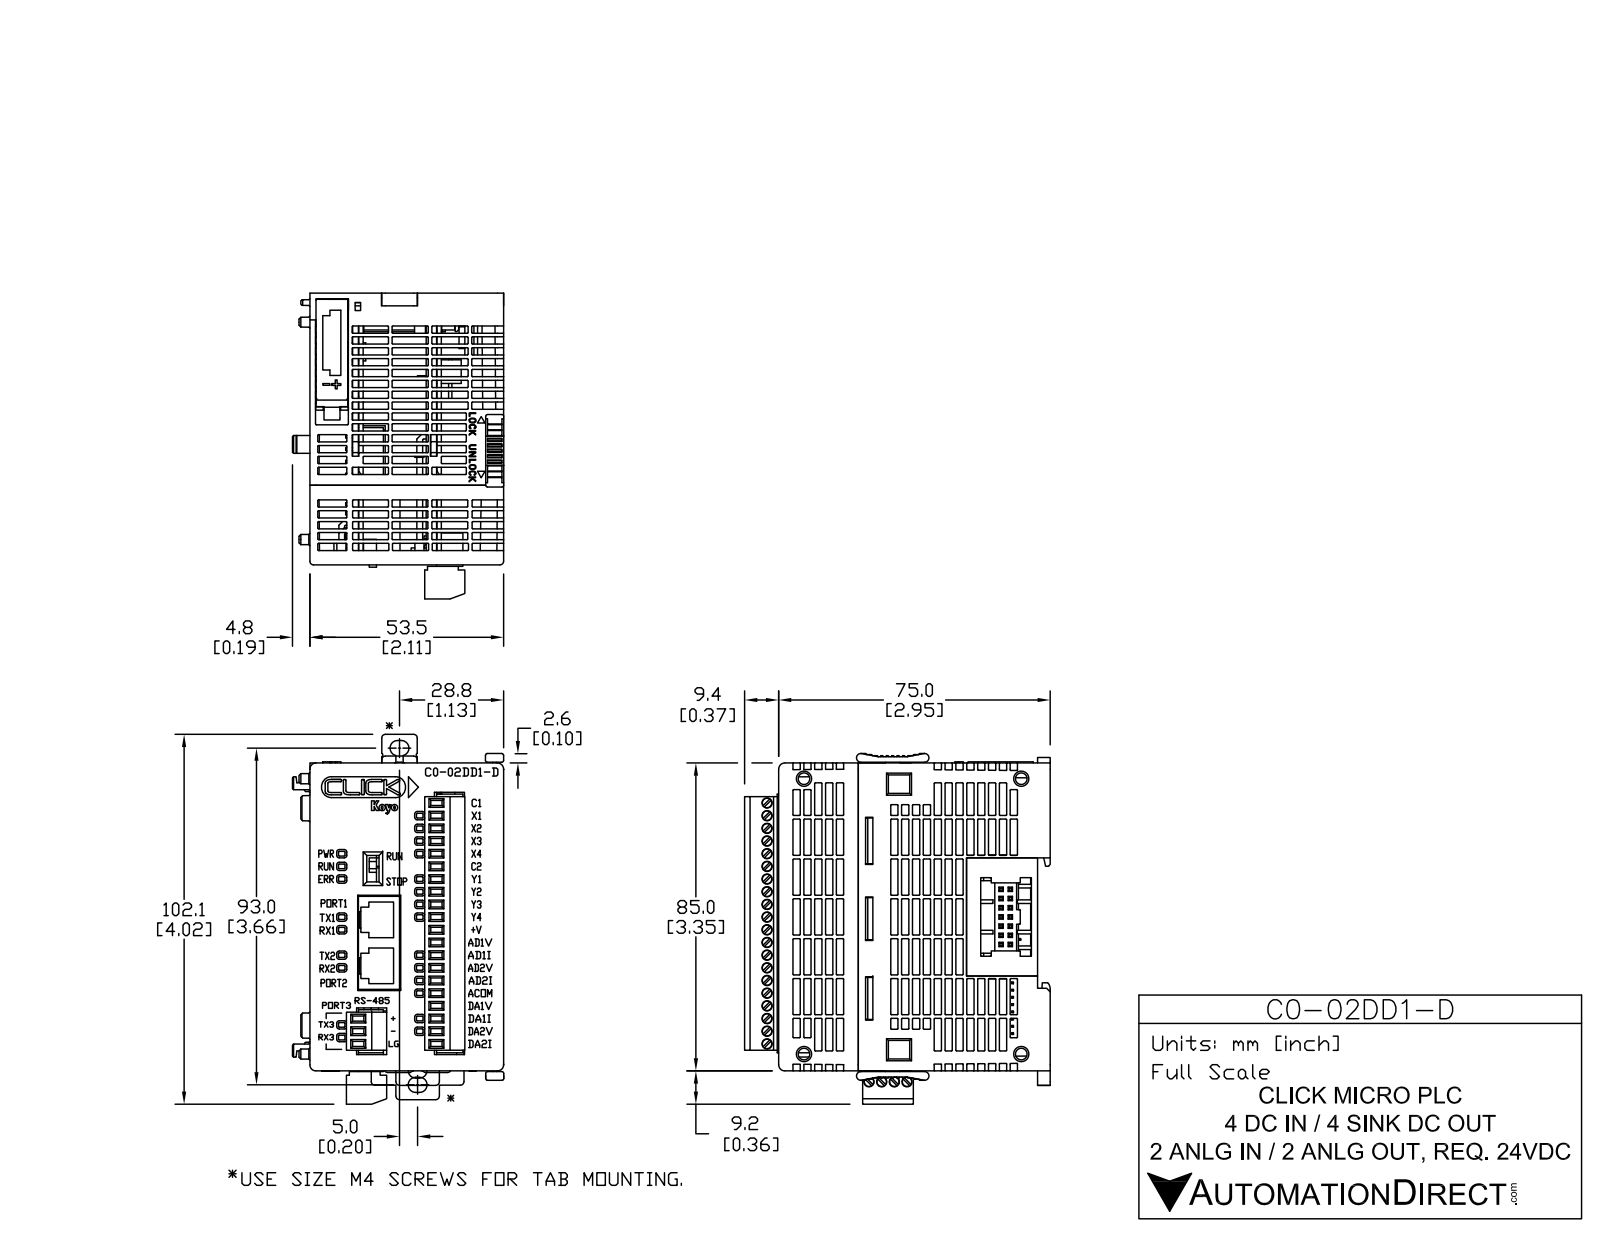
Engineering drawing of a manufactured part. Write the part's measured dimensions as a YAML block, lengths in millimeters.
part_name: "C0-02DD1-D"
step_written_by: "SolidWorks 2009 (AUTOMOTIVE_DESIGN)"
units: millimeters
bodies: {solids: 1, faces: 6070, planar: 4092, cylindrical: 1797, other: 181}
overall_size: [96.8, 84.4, 58.35]
volume: 332445
surface_area: 47010
round_holes:
  - {diameter: 1, count: 27}
  - {diameter: 2.8, count: 27}
  - {diameter: 1.75, count: 1}
  - {diameter: 1.85, count: 1}
  - {diameter: 2.2, count: 1}
round_bosses_or_shafts:
  - {diameter: 2.6, count: 27}
  - {diameter: 2.8, count: 2}
  - {diameter: 2.15, count: 2}
  - {diameter: 1.9, count: 1}
partial_cylinders:
  - {radius: 0.2, count: 867}
  - {radius: 0.3, count: 67}
  - {radius: 0.5, count: 39}
  - {radius: 2.8, count: 27}
  - {radius: 1, count: 11}
  - {radius: 1.2, count: 7}
  - {radius: 1.7, count: 6}
  - {radius: 0.1, count: 5}
face_to_face_distances: [0.5, 53, 71.5, 53.5, 84.5, 85, 52.5, 3.5, 84, 75]
hole_center_spacings: [3.5, 7, 10.5, 14, 17.5, 21, 24.5, 28]
